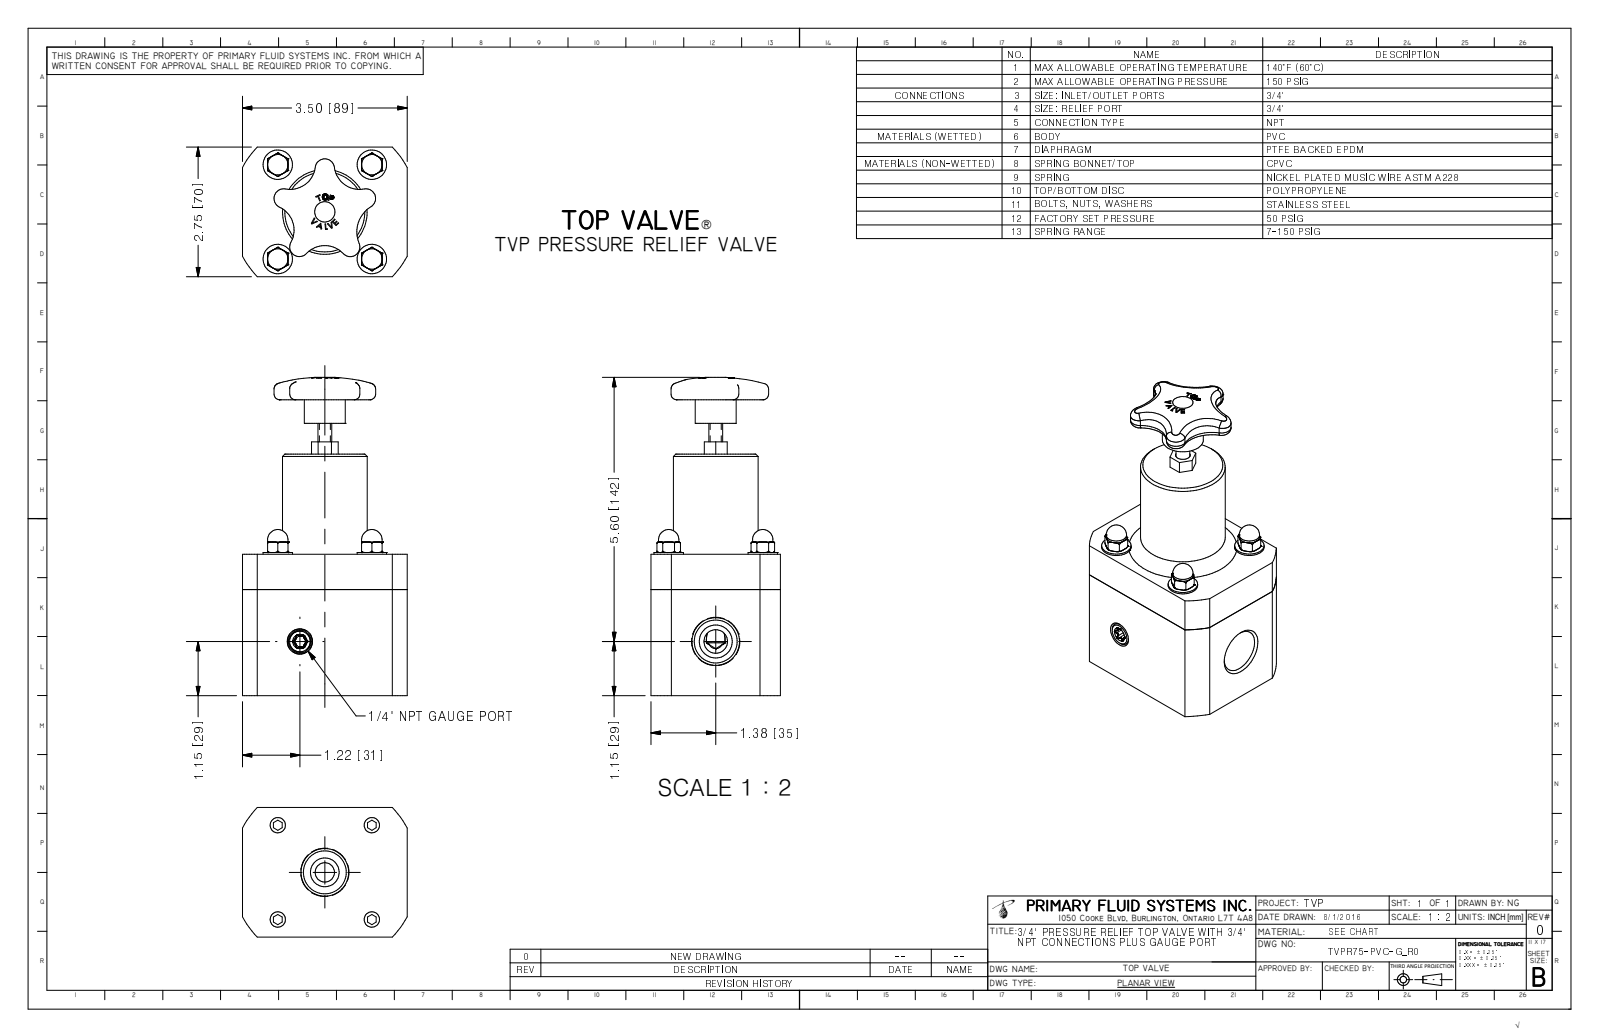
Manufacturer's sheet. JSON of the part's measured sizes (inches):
{"part_name": "TVPR75-PVC-G_R0", "step_written_by": "Autodesk Inventor 2009 (AUTOMOTIVE_DESIGN)", "units": "inches", "bodies": {"solids": 1, "faces": 326, "planar": 131, "cylindrical": 50, "other": 145}, "overall_size": [6.75, 3.5, 2.75], "volume_in3": 33.71, "surface_area_in2": 86.19, "round_holes": [[0.175, 4], [0.911, 2], [2.4, 1]], "round_bosses_or_shafts": [[0.625, 4], [0.433, 4], [2.375, 1], [1.8, 1], [0.87, 1], [0.293, 1]], "partial_cylinders_radius": [[0.027, 6], [0.085, 5], [0.205, 5], [0.536, 4], [0.656, 4], [0.625, 1], [0.745, 1], [1.988, 1]], "face_to_face_distances": [2.75, 3.5, 3, 5.125, 2.125, 0.75, 2.75, 2, 0.6, 2.4], "hole_center_spacings": [1.414, 2, 2.828]}
